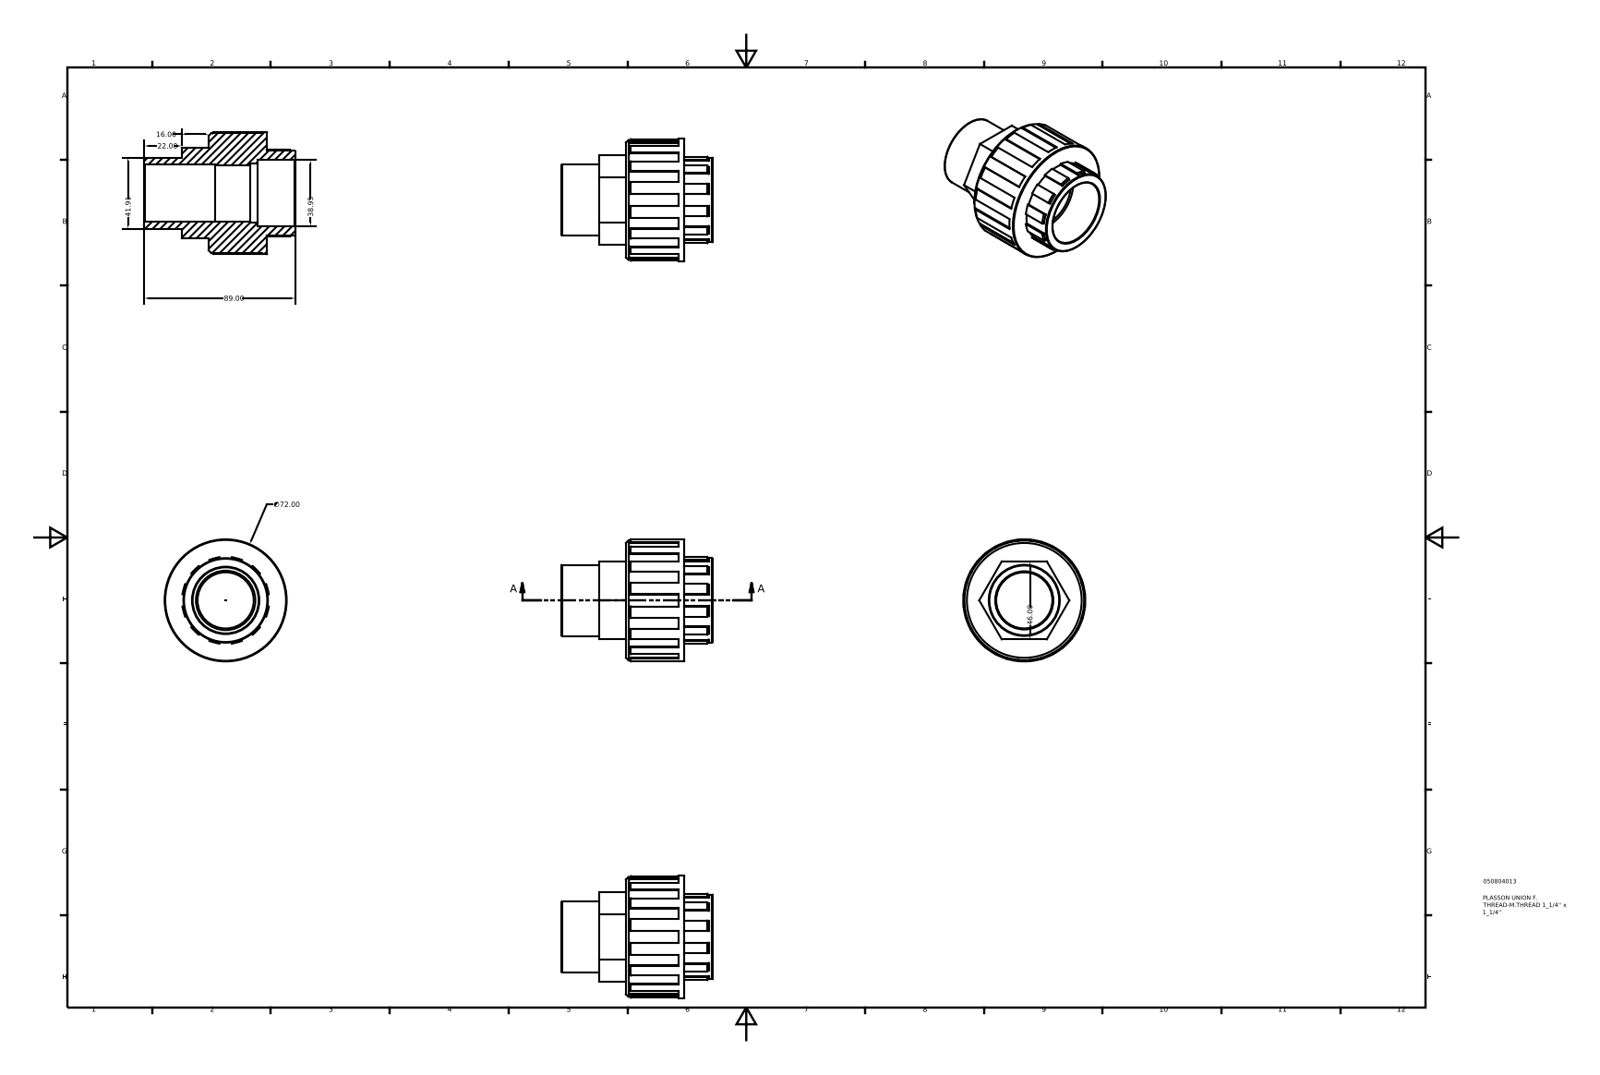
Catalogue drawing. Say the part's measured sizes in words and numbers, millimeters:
The part is named "050804013". Its 3-D file was written by "Autodesk Inventor 2015 (AUTOMOTIVE_DESIGN)". It is 1 solid with 140 faces: 86 planar, 20 cylindrical and 34 other. Overall it measures 89 by 72 by 72 millimeters. Its volume is 144 848 cubic millimeters and its surface area 32 480 square millimeters. Round holes: 1 of diameter 33.11, 1 of diameter 33.53, 1 of diameter 35.06, 1 of diameter 38.95. Round bosses or shafts: 1 of diameter 72, 1 of diameter 70.56, 1 of diameter 49.86, 1 of diameter 41.91. Partial cylindrical surfaces (rounded edges, fillets, slot ends): 1 of radius 25.71. The main face-to-face distances are 34.5, 46, 67, 51, 16.5, 22, 16, 50.5, 38, 72.5.
